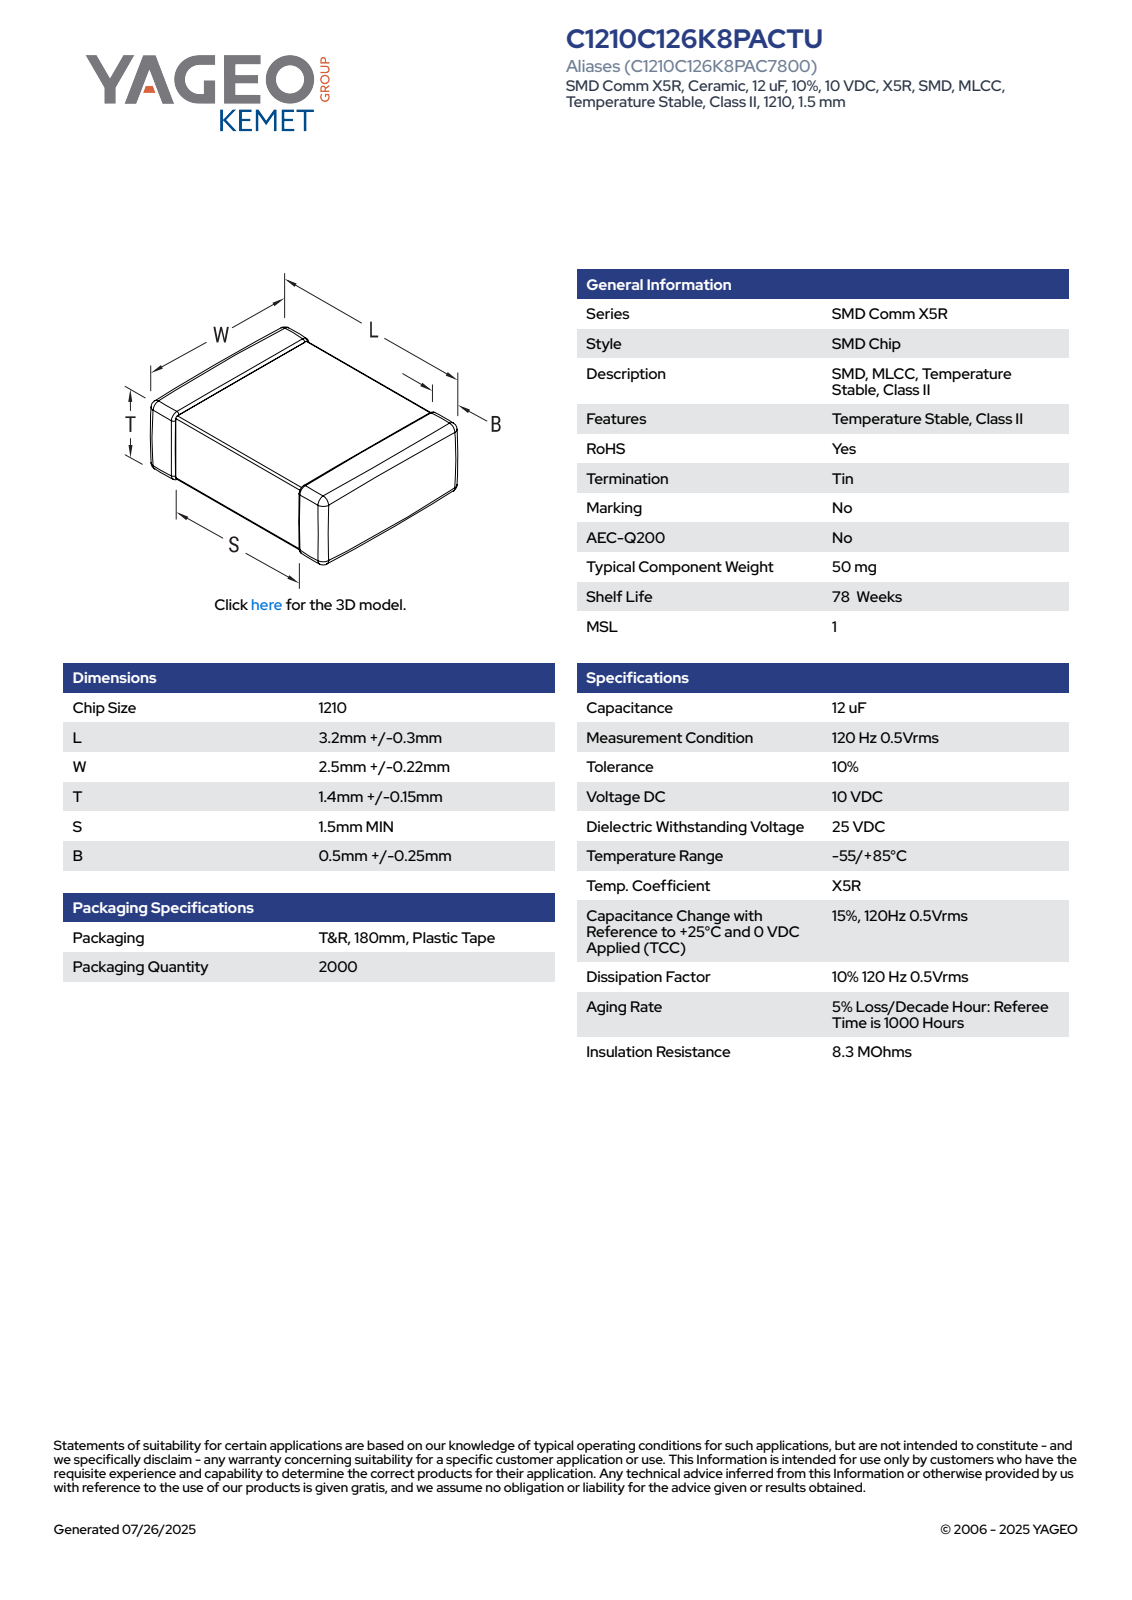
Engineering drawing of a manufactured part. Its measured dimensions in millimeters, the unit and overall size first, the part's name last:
Units: millimetres
Overall size (bounding box): 3.5 × 2.72 × 1.55
Main face-to-face distances: 1.49, 1.43, 3.5, 2.66, 1.55, 2.6, 2.72, 1.5, 1.44, 2.01
Volume: 14 mm³ · Surface area: 38 mm²
Bodies: 4 solids, 125 faces (71 planar, 38 cylindrical, 16 other)
Part name (STEP PRODUCT): CCS_CCSTD_1210_L3.5W2.72T1.55B0.5
STEP written by: SolidWorks 2021 (AUTOMOTIVE_DESIGN)
